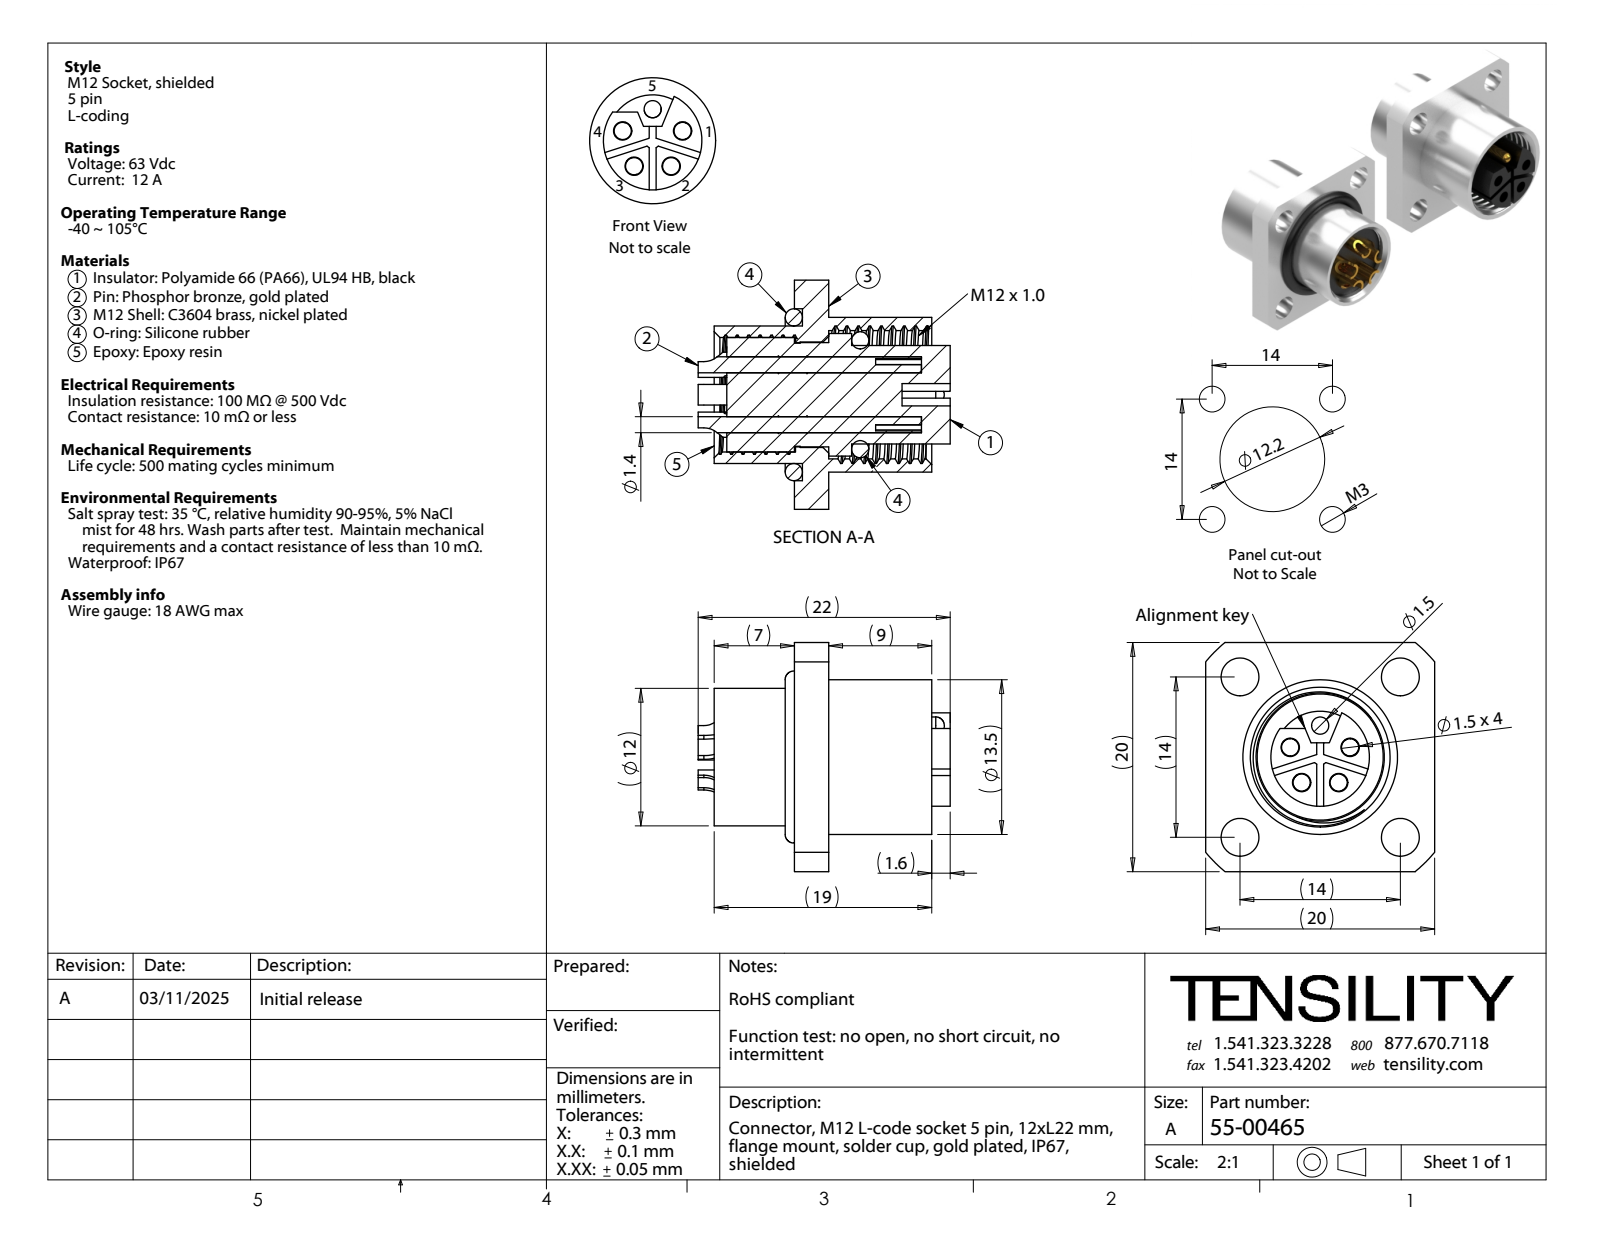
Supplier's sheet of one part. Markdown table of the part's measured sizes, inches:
| quantity | value |
| --- | --- |
| part name | 55-00465-06; 55-00465-04; 55-00465-03; 55-00465-02 (+3 more) |
| STEP written by | SolidWorks 2021 (CONFIG_CONTROL_DESIGN) |
| units | inches |
| bodies | 9 solids, 317 faces (102 planar, 148 cylindrical, 67 other) |
| overall size | 0.866 × 0.787 × 0.787 |
| volume | 0.166 in³ |
| surface area | 7.885 in² |
| round holes (diameter × count) | 0.059 × 5, 0.02 × 4, 0.063 × 4, 0.13 × 4, 0.047 × 1, 0.354 × 1, 0.362 × 1, 0.394 × 1, 0.441 × 1, 0.591 × 1 |
| round bosses / shafts (diameter × count) | 0.087 × 4, 0.531 × 1, 0.472 × 1, 0.421 × 1, 0.358 × 1, 0.339 × 1, 0.071 × 1 |
| partial cylindrical surfaces (radius × count) | 0.073 × 4, 0.067 × 1, 0.512 × 1 |
| main face-to-face distances | 0.118, 0.787, 0.024, 0.35, 0.091, 0.028, 0.26, 0.232, 0.276, 0.472 |
| hole center spacings | 0.108, 0.206, 0.39, 0.551, 0.128, 0.127, 0.283, 0.297 |
